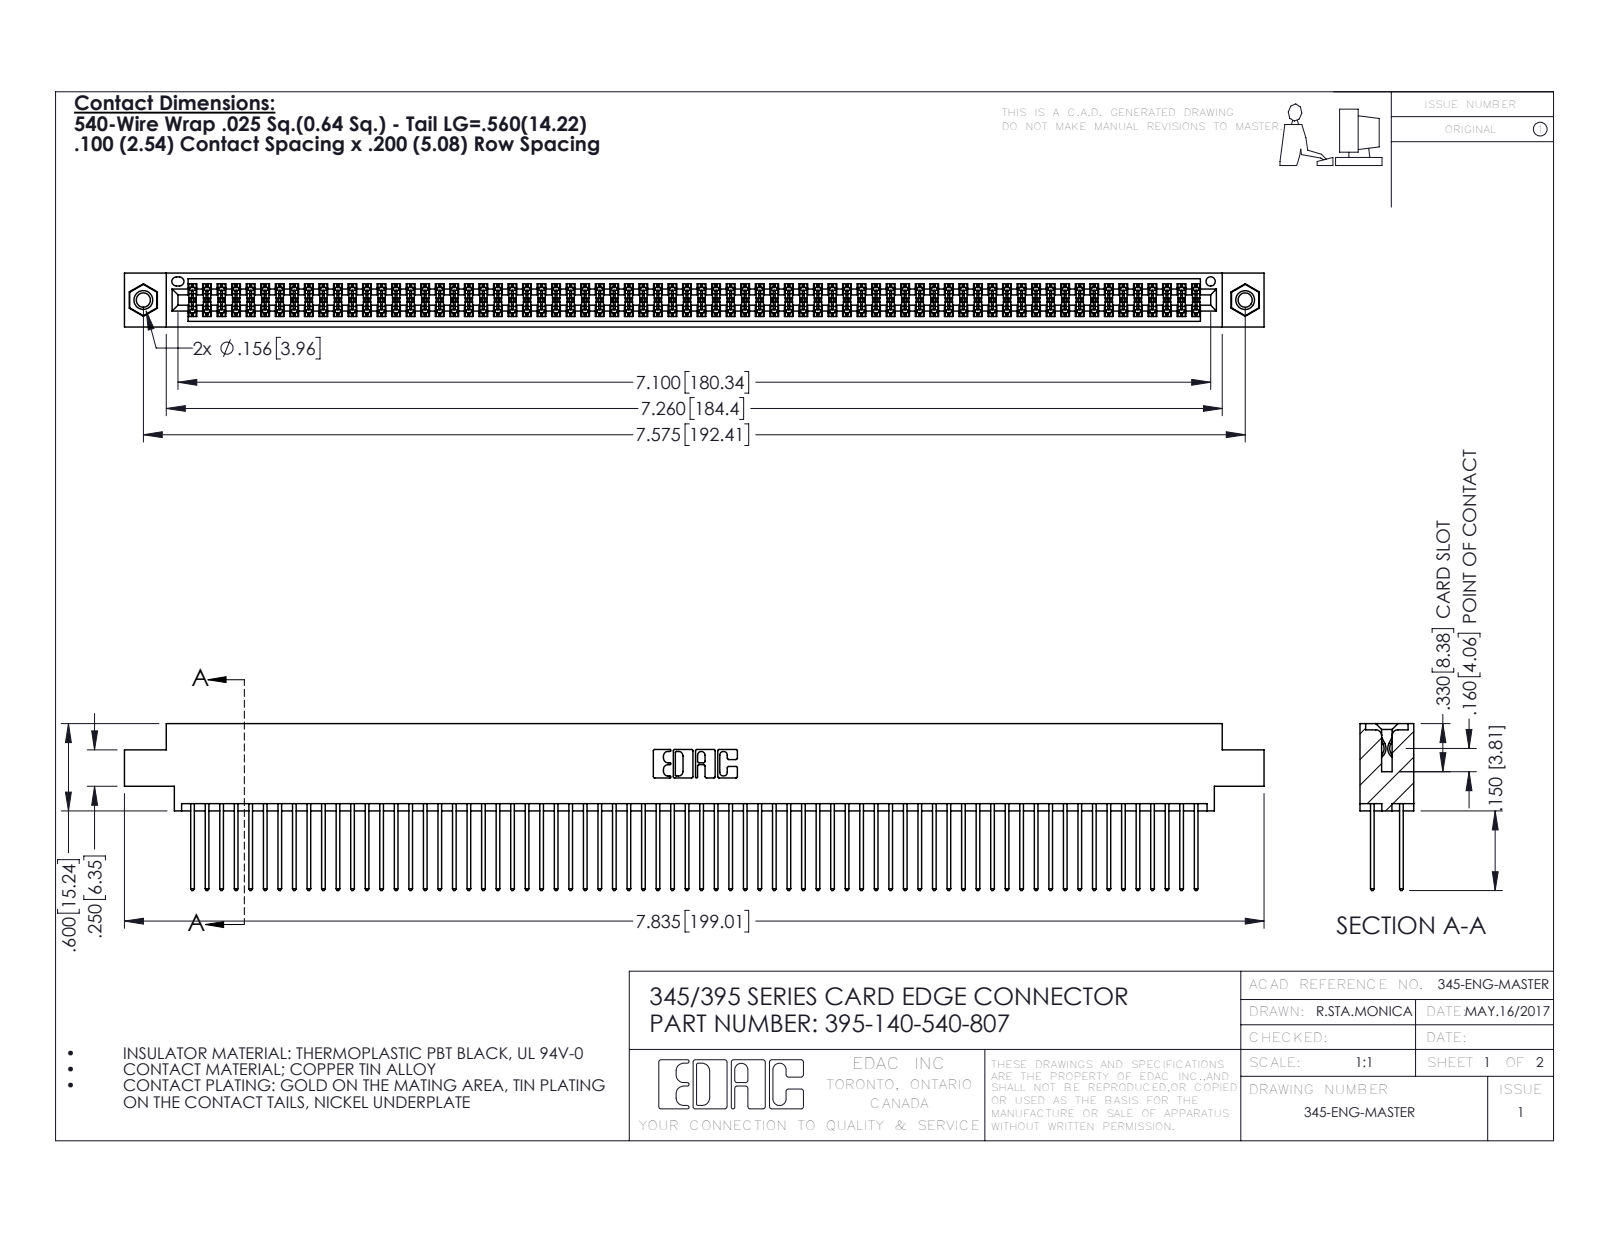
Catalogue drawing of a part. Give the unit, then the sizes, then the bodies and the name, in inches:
Units: inches
Overall size (bounding box): 7.835 × 1.147 × 0.37
Round holes (diameter × count): ⌀0.098 ×2, ⌀0.125 ×2, ⌀0.156 ×2, ⌀0.064 ×1
Round bosses / shafts (diameter × count): ⌀0.155 ×2
Partial cylindrical surfaces — rounded edges, fillets, slot ends (radius × count): R0.006 ×210, R0.01 ×140, R0.01 ×22, R0.007 ×6, R0.031 ×6, R0.026 ×3, R0.014 ×2, R0.019 ×2
Main face-to-face distances: 0.072, 0.298, 0.2, 0.098, 0.272, 0.025, 0.37, 0.225, 0.175, 0.149
Hole centre spacings: 0.27, 7.339, 7.575
Volume: 1.22 in³ · Surface area: 50.74 in²
Bodies: 143 solids, 7190 faces (4736 planar, 2438 cylindrical, 16 other)
Part name (STEP PRODUCT): 345-250-001_345-250-005-103; 345 Part_0.170 Offset - 0.156 Dia-TI; 395-140-540-807; 345-292-001_345-293-140
STEP written by: SolidWorks 2016 (CONFIG_CONTROL_DESIGN)
